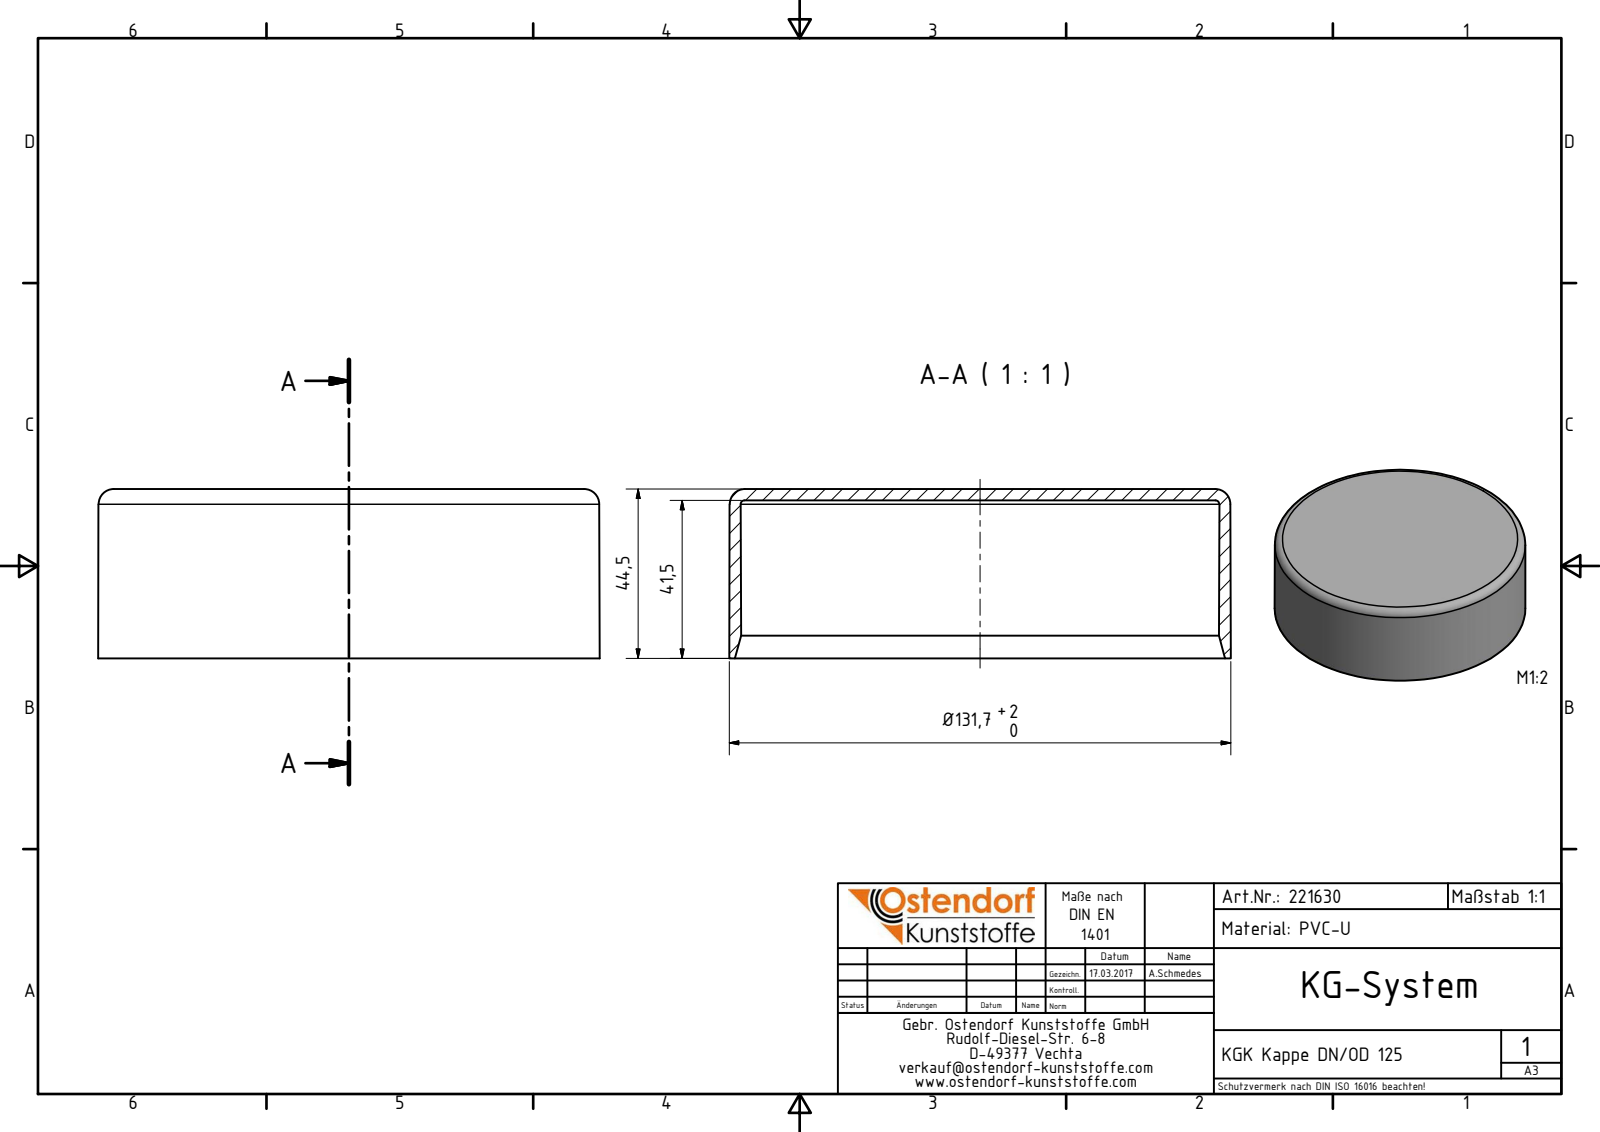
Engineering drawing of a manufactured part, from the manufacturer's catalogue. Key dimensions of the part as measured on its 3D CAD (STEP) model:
Part name (STEP PRODUCT): 221630 KGK Kappe DN_OD 125
STEP written by: Autodesk Inventor 2016 (AUTOMOTIVE_DESIGN)
Units: millimetres
Bodies: 1 solid, 8 faces (3 planar, 0 cylindrical, 5 other)
Overall size (bounding box): 131.7 × 131.7 × 44.5
Volume: 87 998 mm³ · Surface area: 60 604 mm²
Main face-to-face distances: 3, 41.5, 44.5
